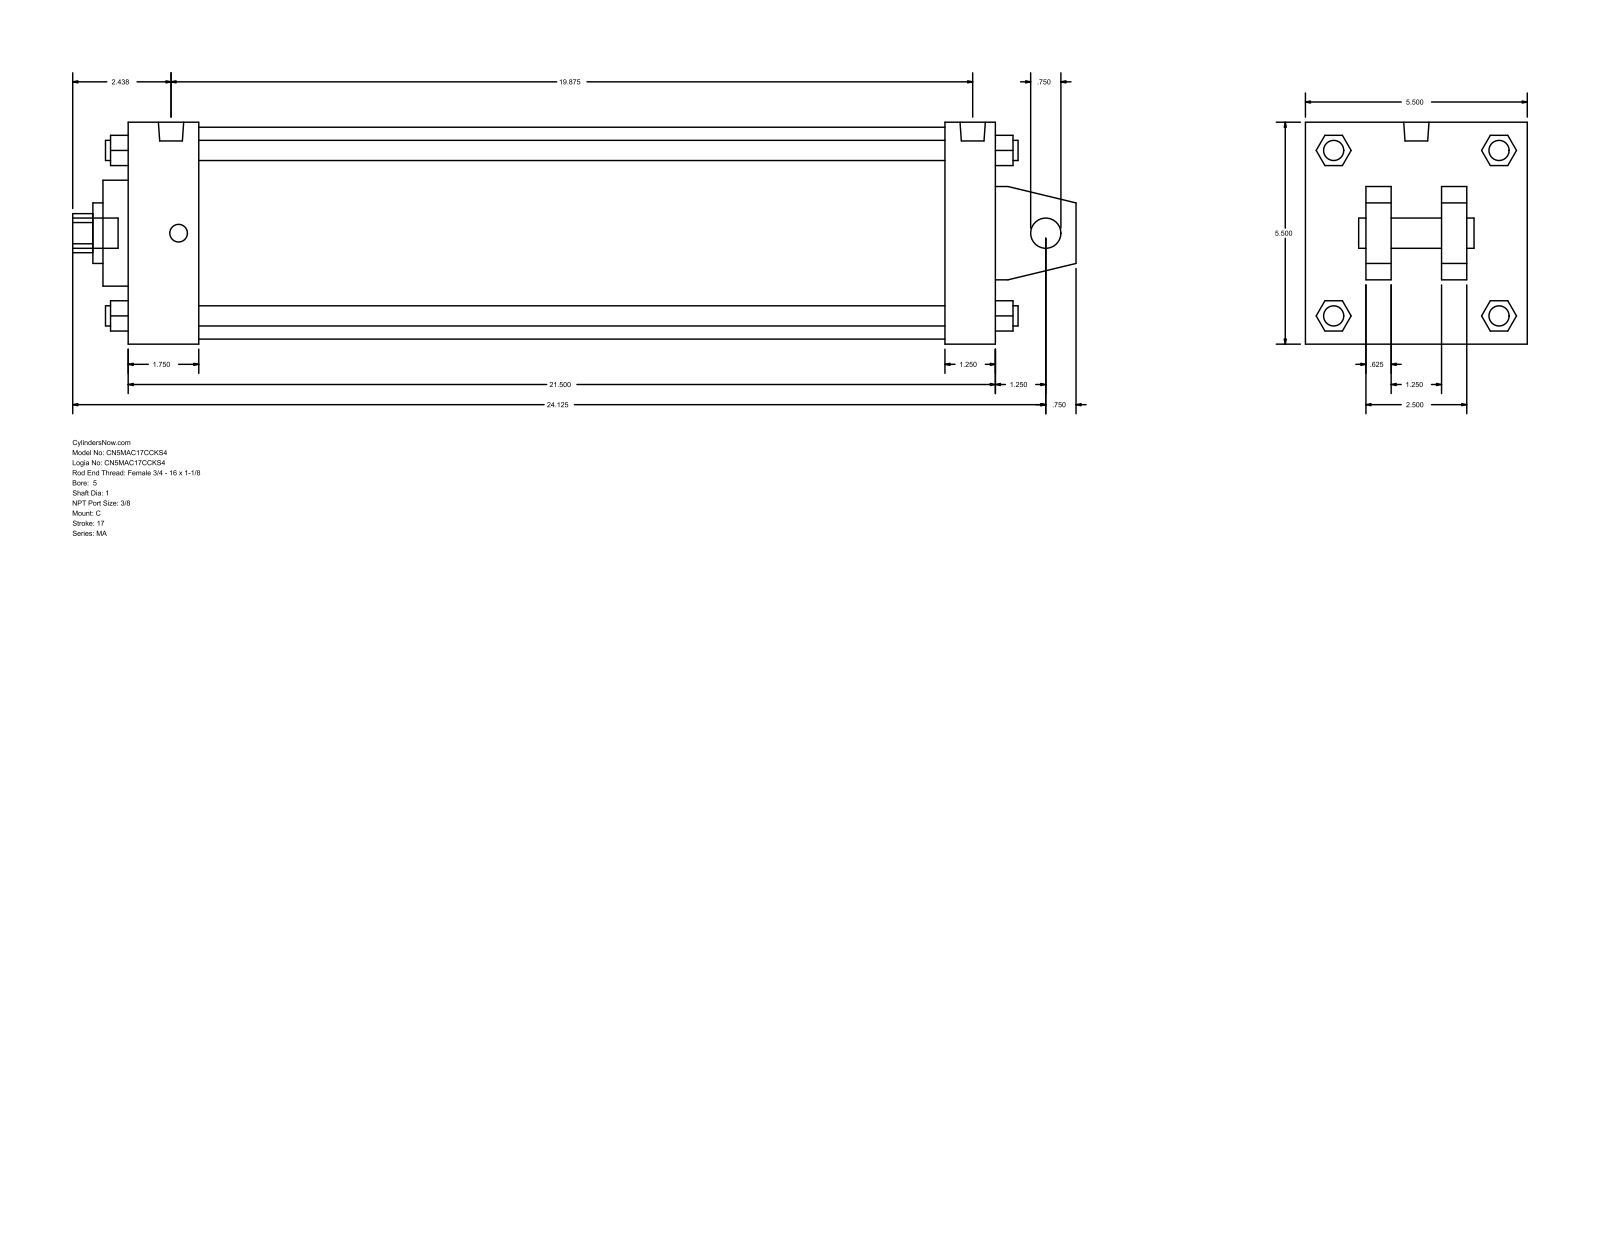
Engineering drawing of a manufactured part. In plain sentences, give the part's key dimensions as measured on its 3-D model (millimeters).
The part is named "MA_C__0500_1". Its 3-D file was written by "GSSL Pune (CONFIG_CONTROL_DESIGN)". It is 0 solids with 141 faces: 109 planar, 32 cylindrical and 0 other. Overall it measures 631.83 by 139.7 by 139.7 millimeters. Round holes: 1 of diameter 19.05, 1 of diameter 25.4, 1 of diameter 38.1, 1 of diameter 66.67, 1 of diameter 133.35. Round bosses or shafts: 4 of diameter 12.7, 4 of diameter 11.11, 2 of diameter 15.93, 1 of diameter 19.05. Partial cylindrical surfaces (rounded edges, fillets, slot ends): 1 of radius 12.29. The main face-to-face distances are 139.7, 546.1, 15.87, 514.35, 31.75, 44.46, 469.89, 501.64, 38.1, 101.6.
